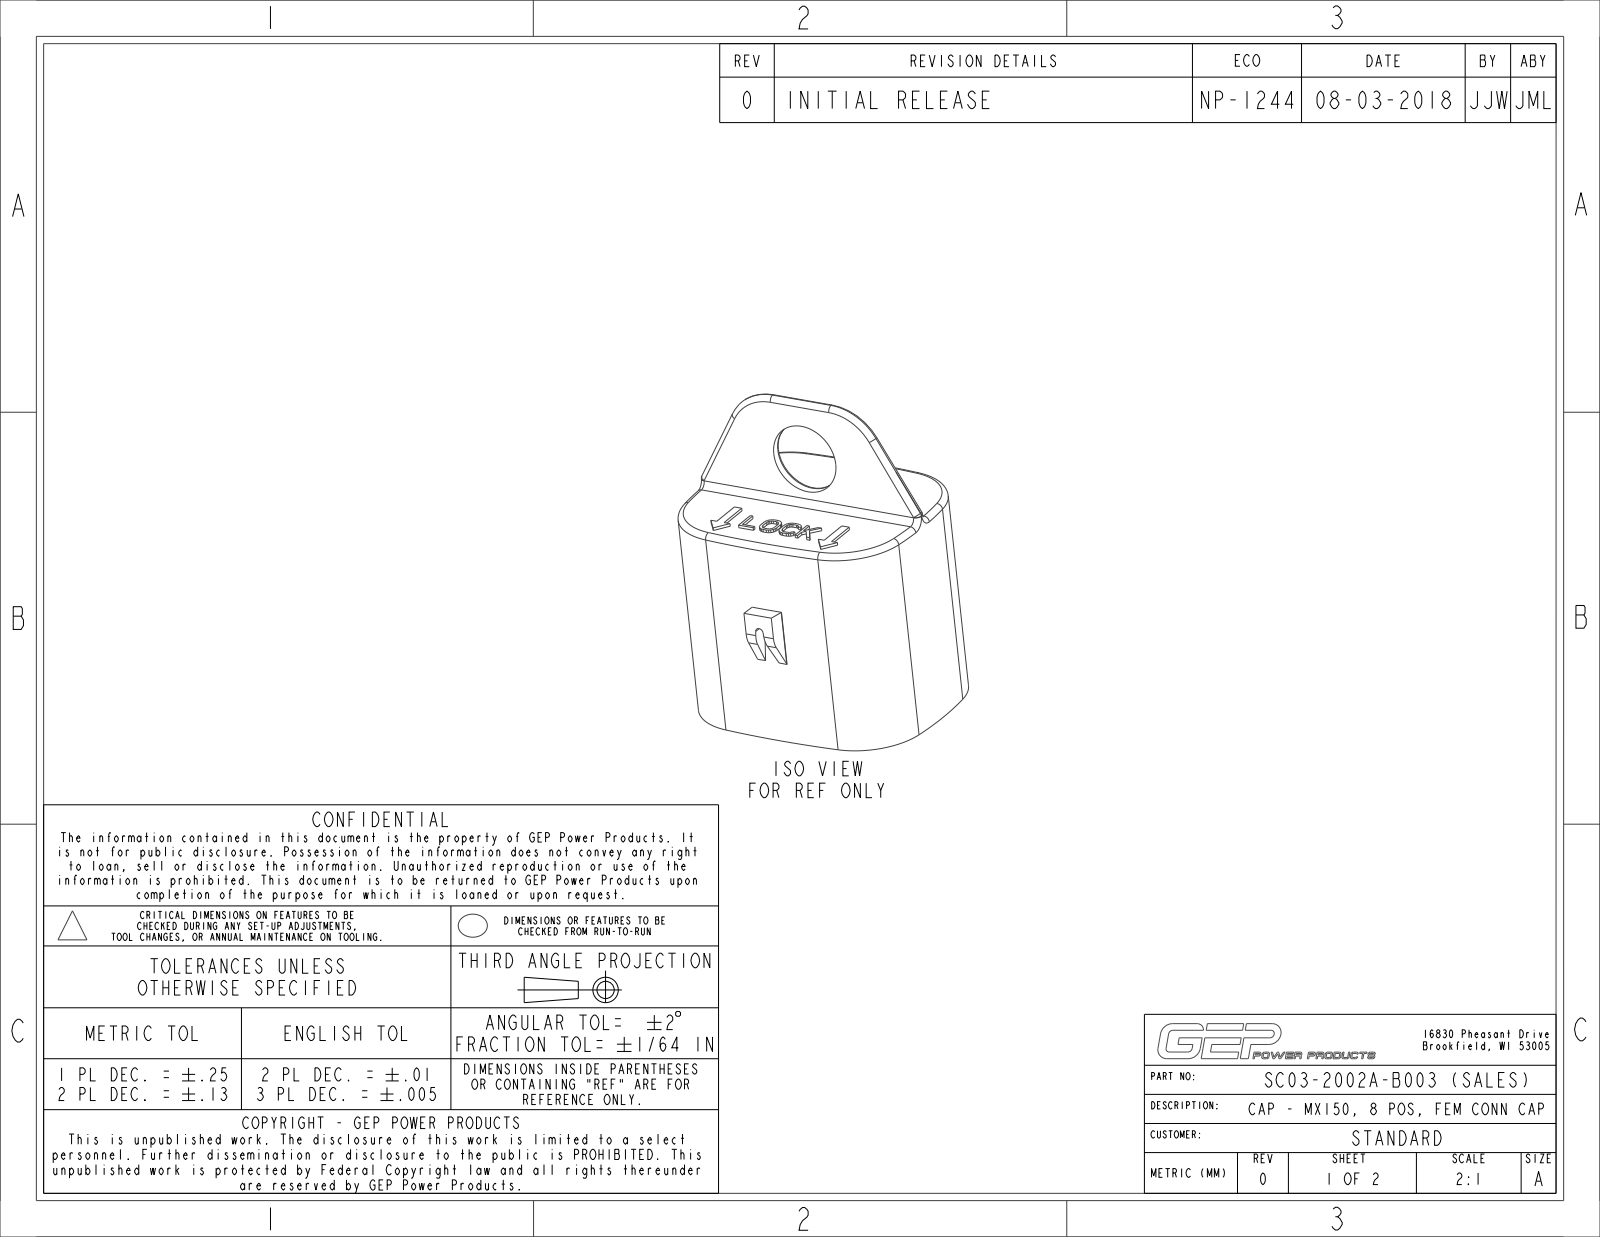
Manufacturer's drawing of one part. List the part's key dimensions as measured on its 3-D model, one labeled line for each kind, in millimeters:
Part name (STEP PRODUCT): PC03-2002A-B003_NCF; SC03-2002A-B003_NCF_ASM
STEP written by: CREO PARAMETRIC BY PTC INC, 2017110 (CONFIG_CONTROL_DESIGN)
Units: millimetres
Bodies: 1 solid, 476 faces (287 planar, 33 cylindrical, 156 other)
Overall size (bounding box): 29 × 22.44 × 19.47
Volume: 2 054 mm³ · Surface area: 3 448 mm²
Round holes (diameter × count): ⌀3 ×1, ⌀6.35 ×1
Partial cylindrical surfaces — rounded edges, fillets, slot ends (radius × count): R5.72 ×4, R0.5 ×3, R0.3 ×2, R0.6 ×2, R31.73 ×2, R77.82 ×2, R0.38 ×1, R2 ×1
Main face-to-face distances: 1, 18, 19, 18.15, 0.85, 1.1, 19.25, 1.25, 18.25, 0.75
